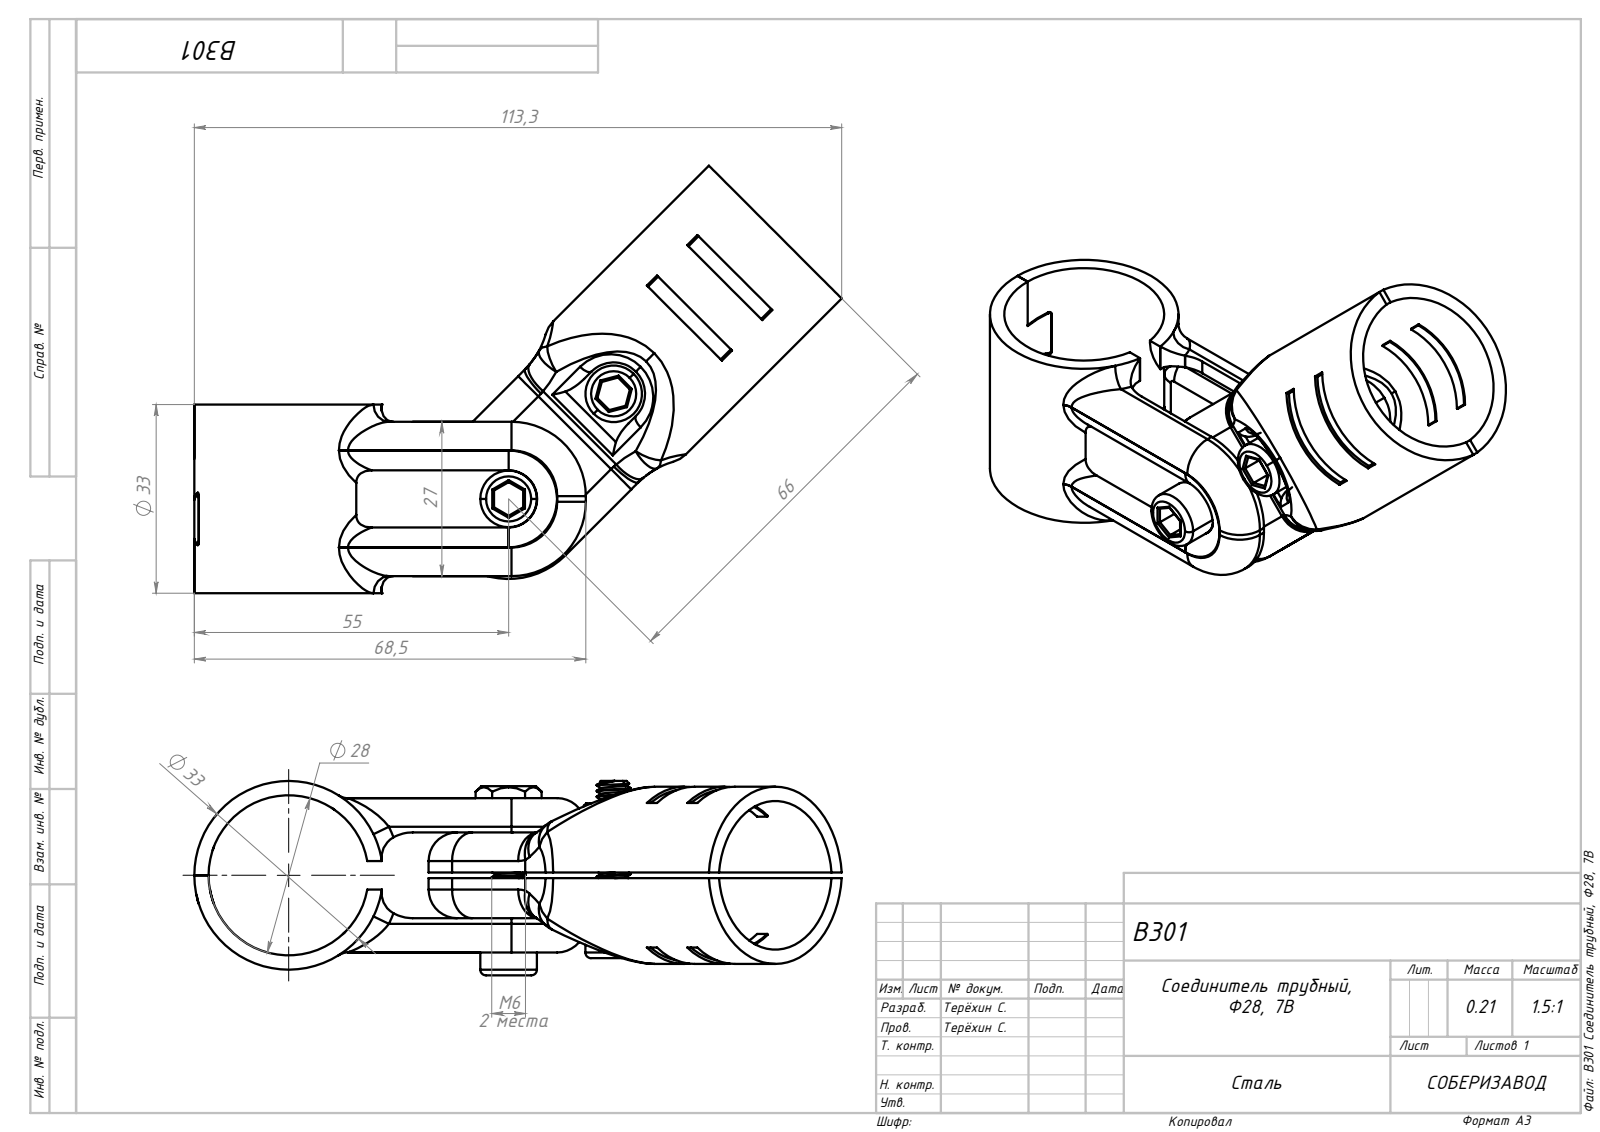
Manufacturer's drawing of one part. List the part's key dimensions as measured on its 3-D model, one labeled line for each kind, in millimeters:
Part name (STEP PRODUCT): B301 Соединитель трубный, Ф28, 7B
STEP written by: SolidWorks 2022 (AUTOMOTIVE_DESIGN)
Units: millimetres
Bodies: 8 solids, 562 faces (150 planar, 258 cylindrical, 154 other)
Overall size (bounding box): 113.29 × 74.79 × 34
Volume: 30 525 mm³ · Surface area: 28 469 mm²
Round holes (diameter × count): ⌀5.3 ×2, ⌀7.4 ×1, ⌀8 ×1, ⌀8.05 ×1, ⌀28 ×1
Round bosses / shafts (diameter × count): ⌀9.9 ×2, ⌀7 ×2, ⌀5.9 ×2, ⌀33 ×1
Partial cylindrical surfaces — rounded edges, fillets, slot ends (radius × count): R5 ×14, R0.3 ×12, R4 ×12, R2.5 ×10, R0.5 ×8, R14 ×5, R1.5 ×4, R2 ×4
Main face-to-face distances: 2.5, 8, 4, 16.5, 5.5, 12.5, 4.5, 7, 1, 10
Hole centre spacings: 25.99
